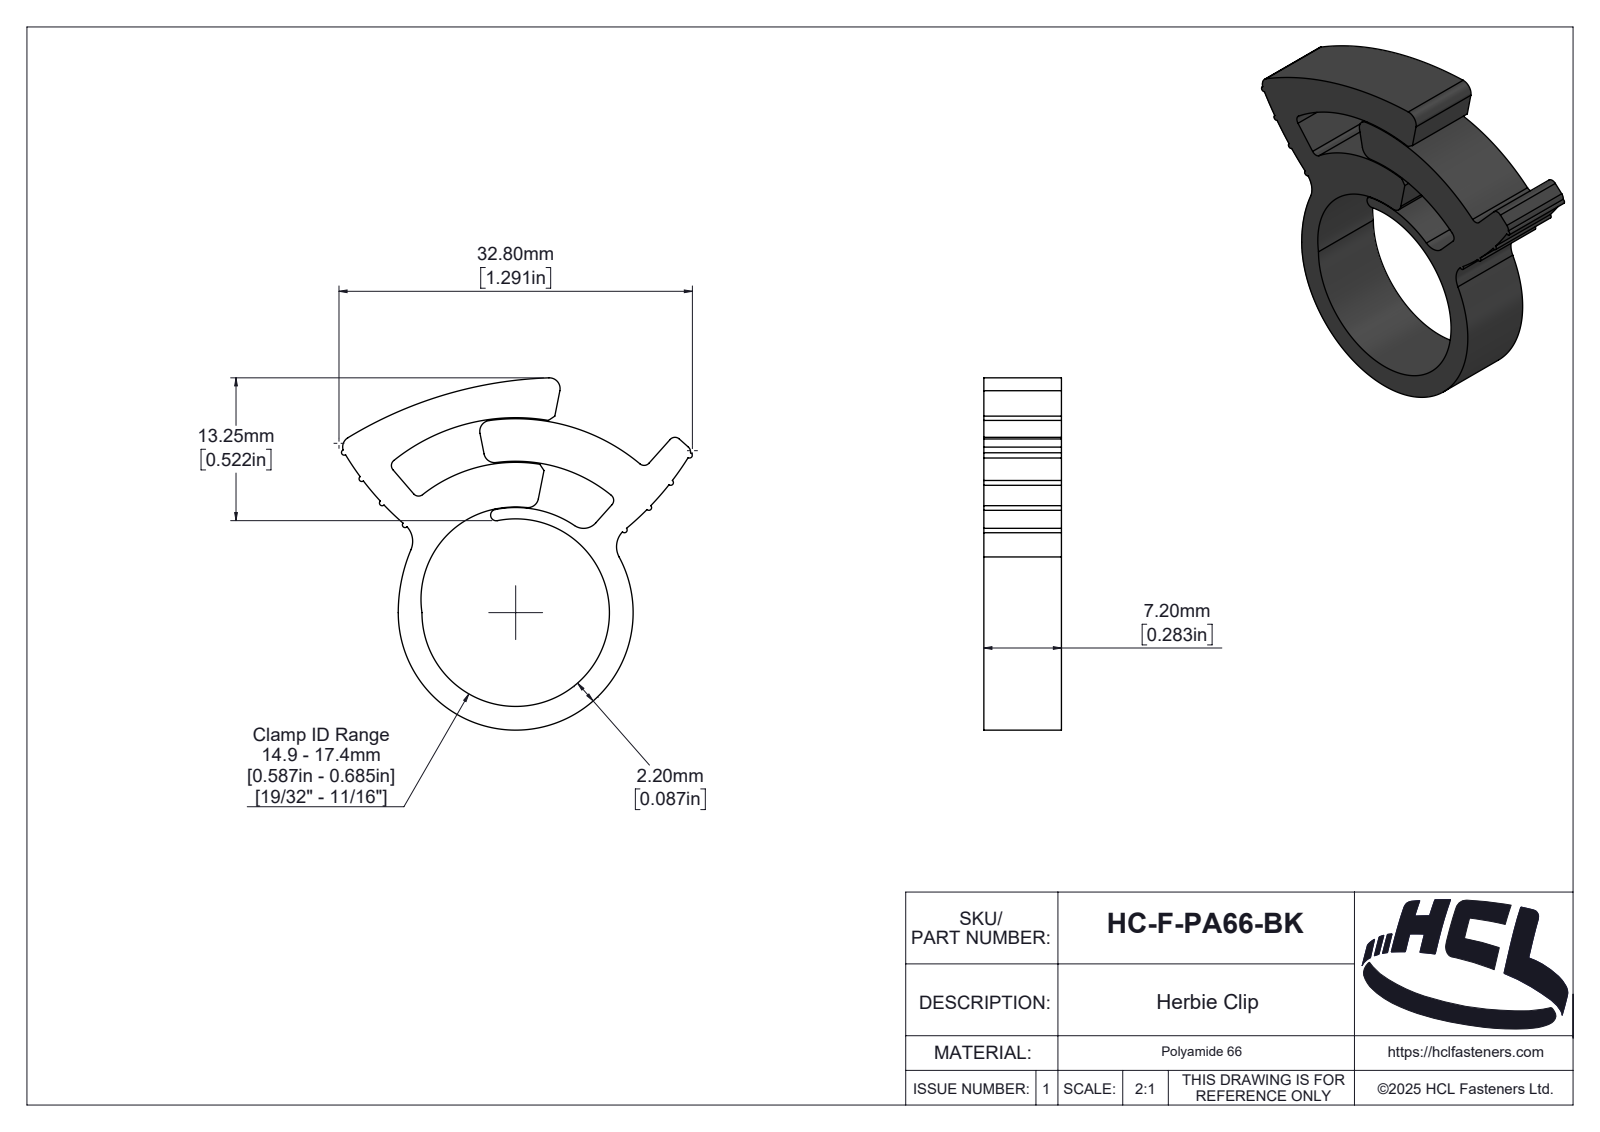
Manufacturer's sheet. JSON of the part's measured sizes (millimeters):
{"part_name": "HC-F-PA66-BK", "step_written_by": "SolidWorks 2025 (AUTOMOTIVE_DESIGN)", "units": "millimeters", "bodies": {"solids": 1, "faces": 162, "planar": 13, "cylindrical": 100, "other": 49}, "overall_size": [32.68, 32.56, 7.2], "volume_mm3": 2431, "surface_area_mm2": 2448, "partial_cylinders_radius": [[0.25, 8], [0.6, 6], [1, 5], [2, 2], [15.03, 2], [0.17, 1], [0.53, 1], [0.67, 1]], "face_to_face_distances": [7.2]}
